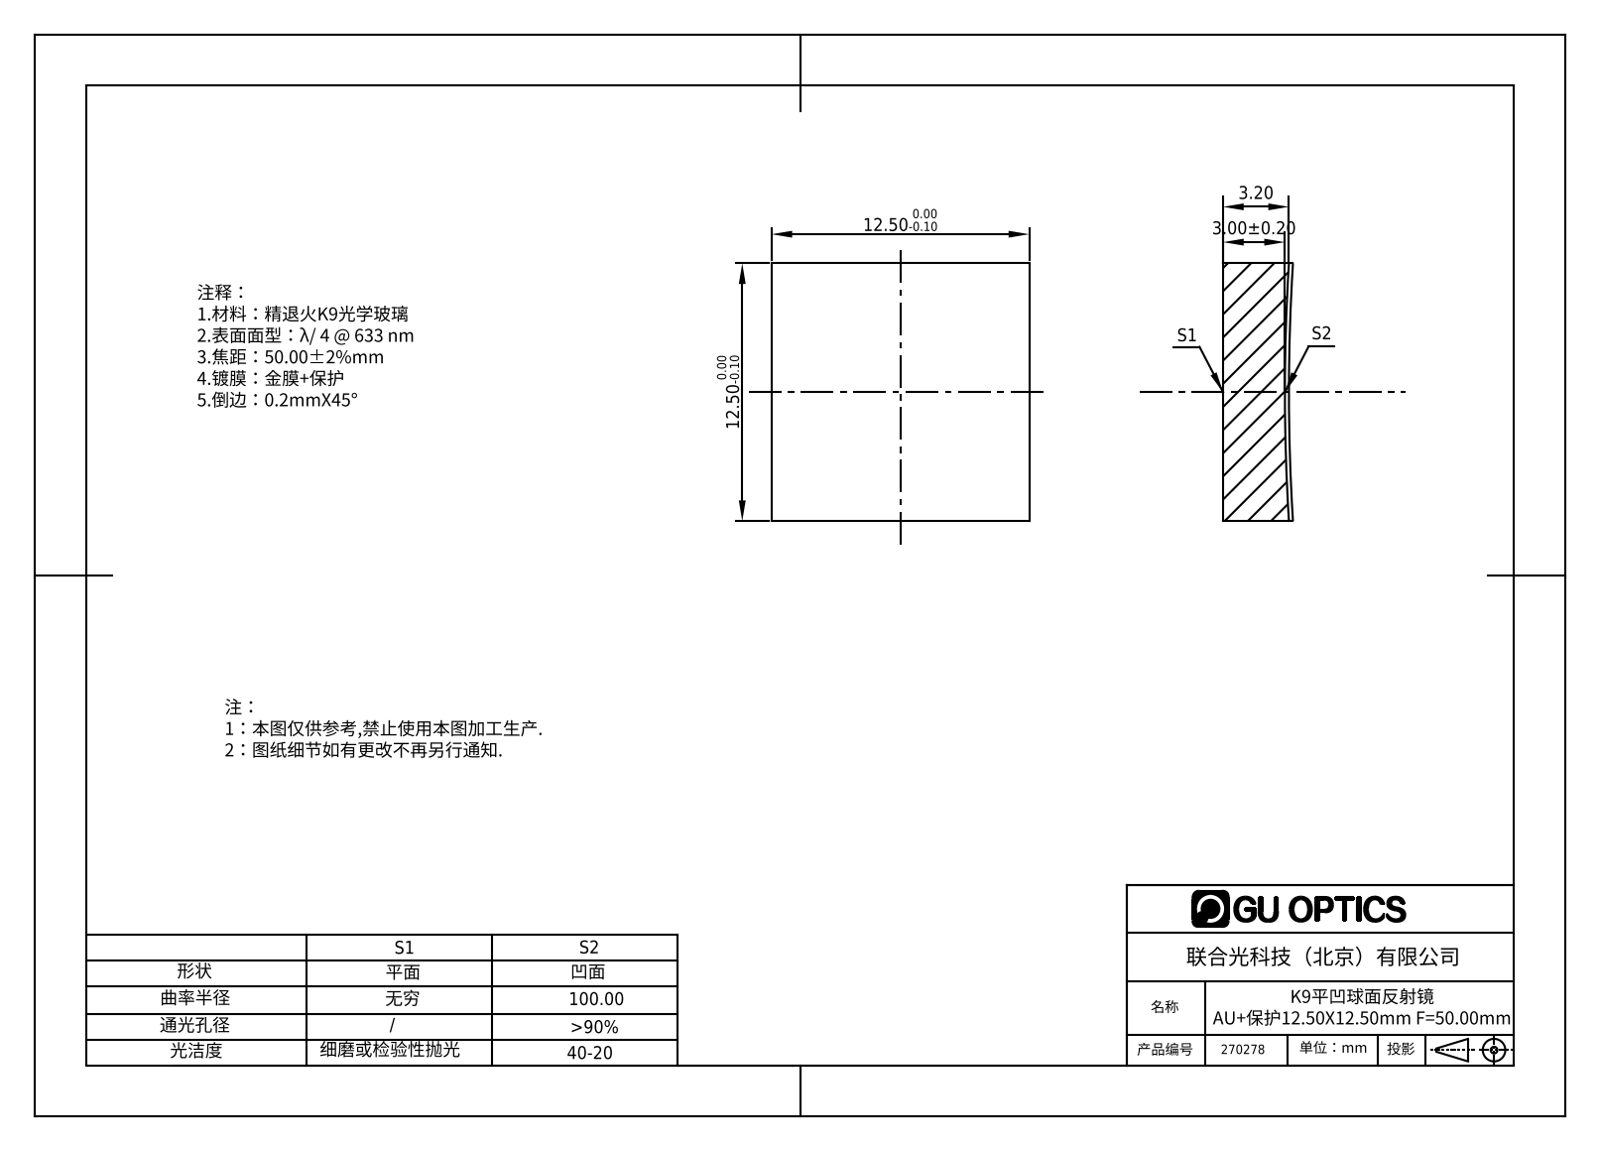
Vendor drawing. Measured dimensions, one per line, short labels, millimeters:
name: 270018
written by: SolidWorks 2019 (AUTOMOTIVE_DESIGN)
unit: mm
bodies: 1 solid, 7 faces (5 planar, 0 cylindrical, 2 other)
size: 12.5 × 12.5 × 3.39
volume: 489 mm³; area: 476 mm²
face distances: 12.5
